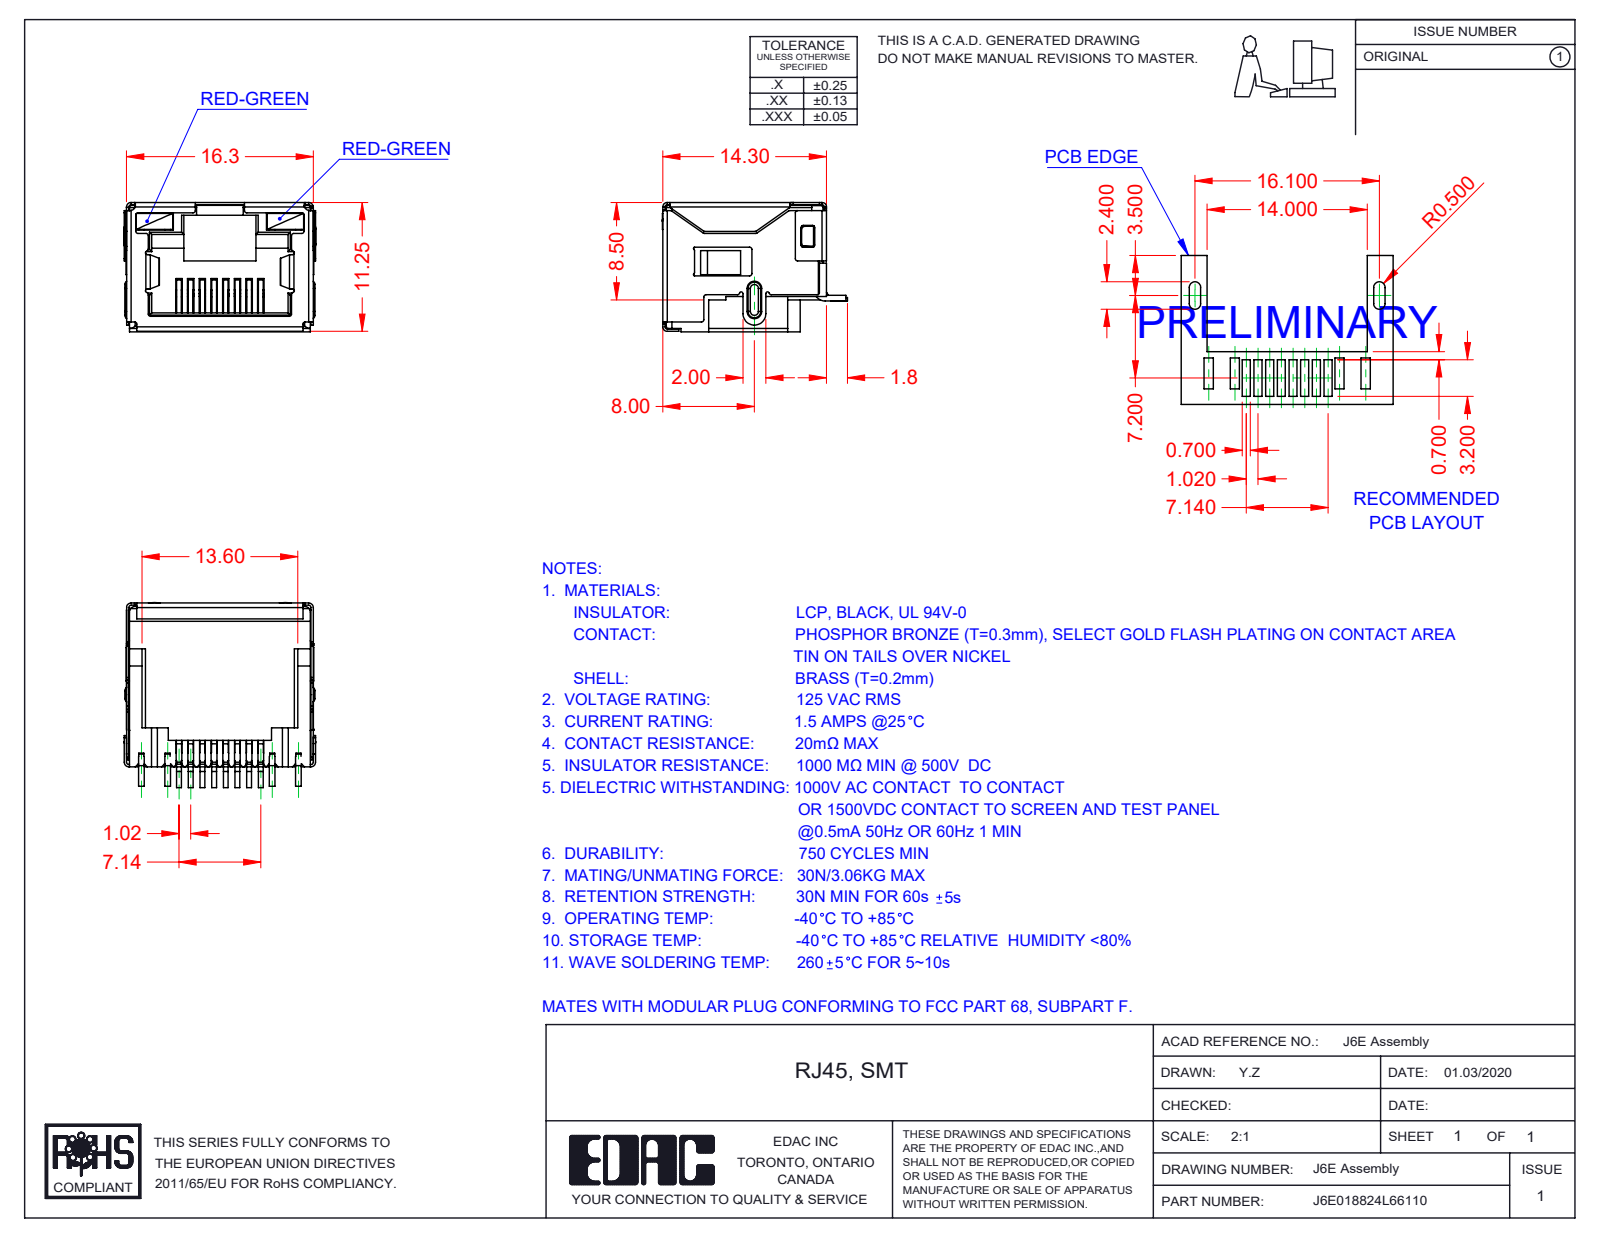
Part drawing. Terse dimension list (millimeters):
name: J6E018824L66110; 6E LED RH_6-Red-Green; 6E Contacts; 6E Insulator_LED (+2 more)
written by: SolidWorks 2016 (CONFIG_CONTROL_DESIGN)
unit: mm
bodies: 12 solids, 1500 faces (1099 planar, 351 cylindrical, 50 other)
size: 16.75 × 16.15 × 11.3
volume: 1 109 mm³; area: 4 045 mm²
rounds: 82× R0.2, 17× R0.25, 13× R0.4, 13× R0.5, 10× R0.1, 7× R0.15, 4× R0.3, 3× R1
face distances: 11.05, 16.05, 16.1, 15.85, 11.1, 11.3, 2.4, 0.7, 9.85, 0.49
